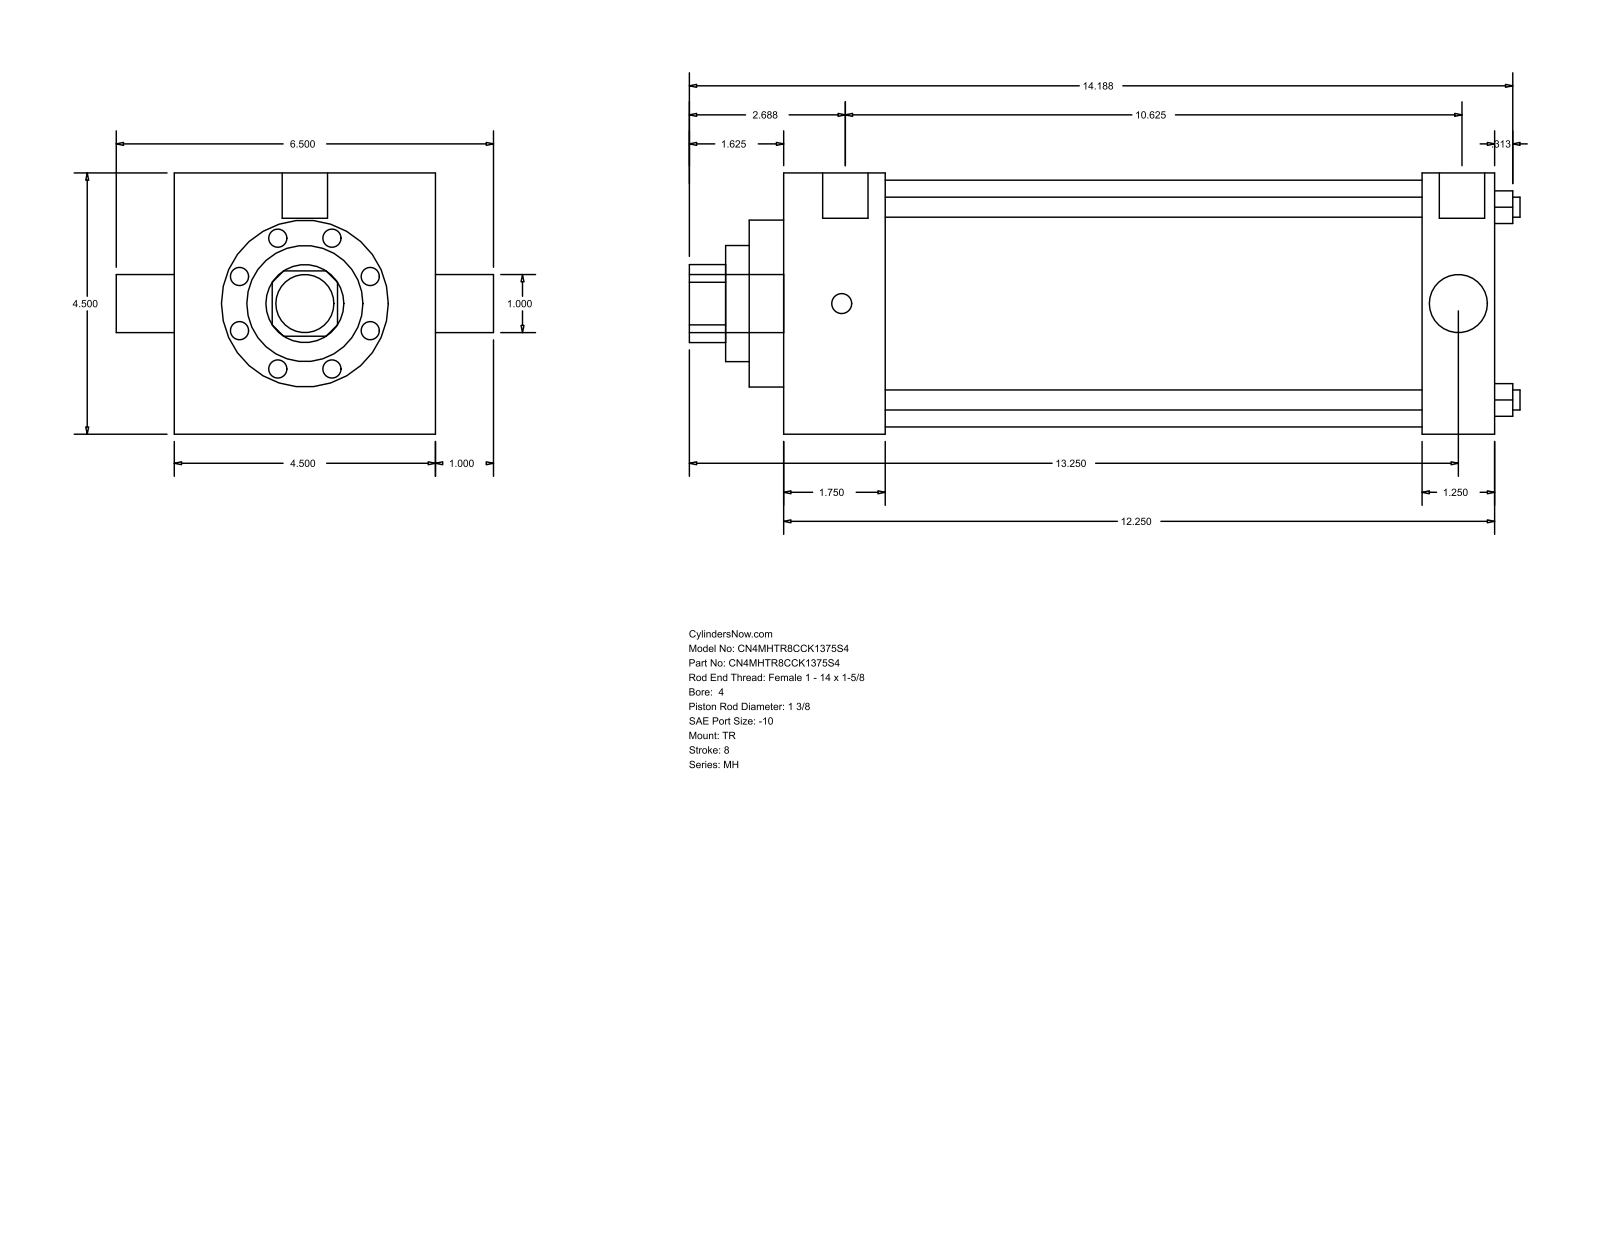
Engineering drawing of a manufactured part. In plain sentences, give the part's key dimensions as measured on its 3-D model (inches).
The part is named "MH_TR__0400_1.375". Its 3-D file was written by "GSSL Pune (CONFIG_CONTROL_DESIGN)". It is 0 solids with 86 faces: 61 planar, 25 cylindrical and 0 other. Overall it measures 14.313 by 6.5 by 4.5 inches. Round holes: 4 of diameter 0.345, 1 of diameter 1, 1 of diameter 1.375, 1 of diameter 2, 1 of diameter 2.875, 1 of diameter 4.25. Round bosses or shafts: 3 of diameter 0.344, 2 of diameter 0.781, 1 of diameter 1. Partial cylindrical surfaces (rounded edges, fillets, slot ends): 1 of radius 0.672. The main face-to-face distances are 4.5, 12.25, 1.75, 10.5, 11, 9.25, 1.25, 0.594, 2.344, 11.594. The hole center spacings are 2.347, 3.32, 4.695.
